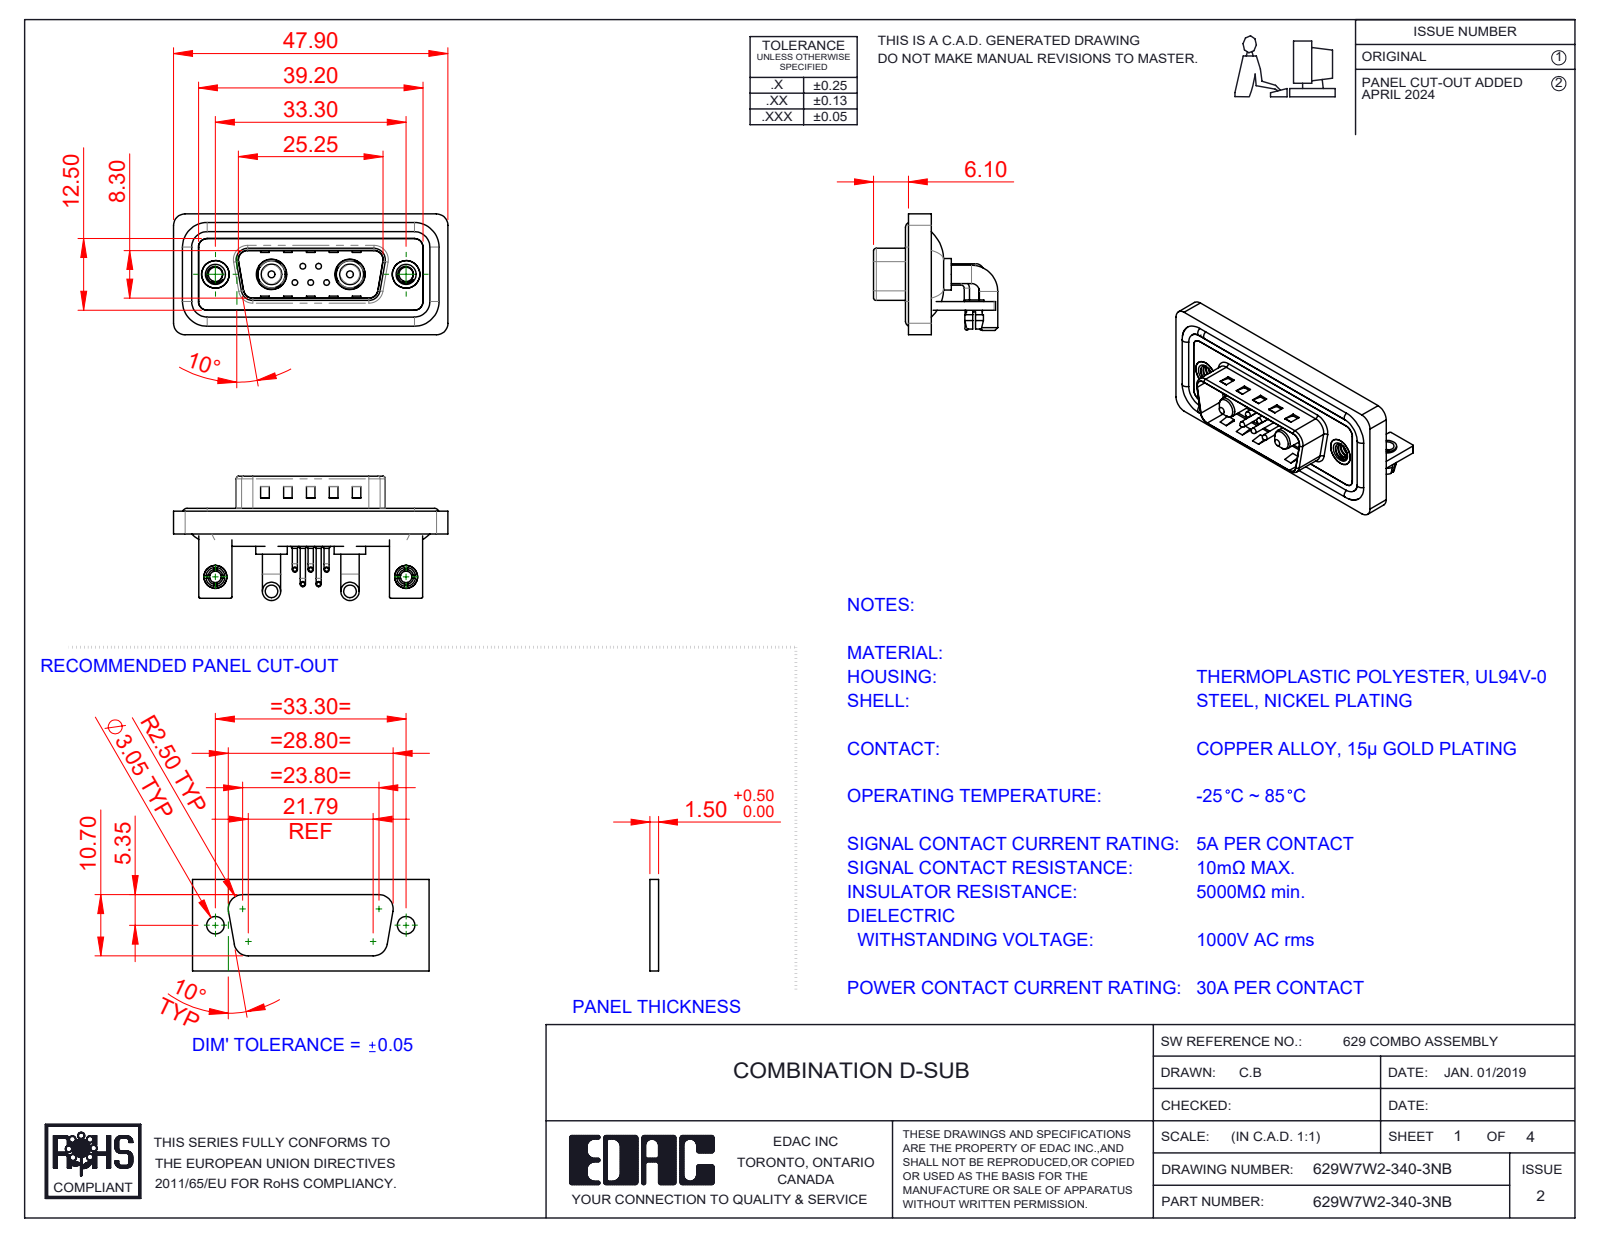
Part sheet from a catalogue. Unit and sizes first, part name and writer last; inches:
Units: inches
Overall size (bounding box): 1.886 × 0.854 × 0.831
Round holes (diameter × count): ⌀0.079 ×7, ⌀0.03 ×5, ⌀0.063 ×5, ⌀0.098 ×4, ⌀0.126 ×2, ⌀0.157 ×2, ⌀0.189 ×2, ⌀0.191 ×2, ⌀0.197 ×2, ⌀0.209 ×2
Round bosses / shafts (diameter × count): ⌀0.035 ×10, ⌀0.059 ×5, ⌀0.039 ×5, ⌀0.026 ×5, ⌀0.126 ×4, ⌀0.063 ×4, ⌀0.217 ×2, ⌀0.205 ×2
Partial cylindrical surfaces — rounded edges, fillets, slot ends (radius × count): R0.079 ×21, R0.059 ×18, R0.01 ×16, R0.02 ×9, R0.063 ×8, R0.04 ×5, R0.024 ×4, R0.026 ×4
Main face-to-face distances: 0.016, 0.059, 0.031, 0.114, 0.083, 0.043, 0.063, 0.047, 0.146, 0.177
Hole centre spacings: 0.124, 0.109, 0.386, 0.925, 1.311, 0.17, 0.17, 0.198
Volume: 0.369 in³ · Surface area: 15.46 in²
Bodies: 20 solids, 1213 faces (585 planar, 456 cylindrical, 172 other)
Part name (STEP PRODUCT): Power Pin_30A RA; 629Combo Shell Front_15 Contacts; 629Combo Stabilizer Bracket; 629Combo Contact Row 1 (+7 more)
STEP written by: SolidWorks 2023 (CONFIG_CONTROL_DESIGN)
